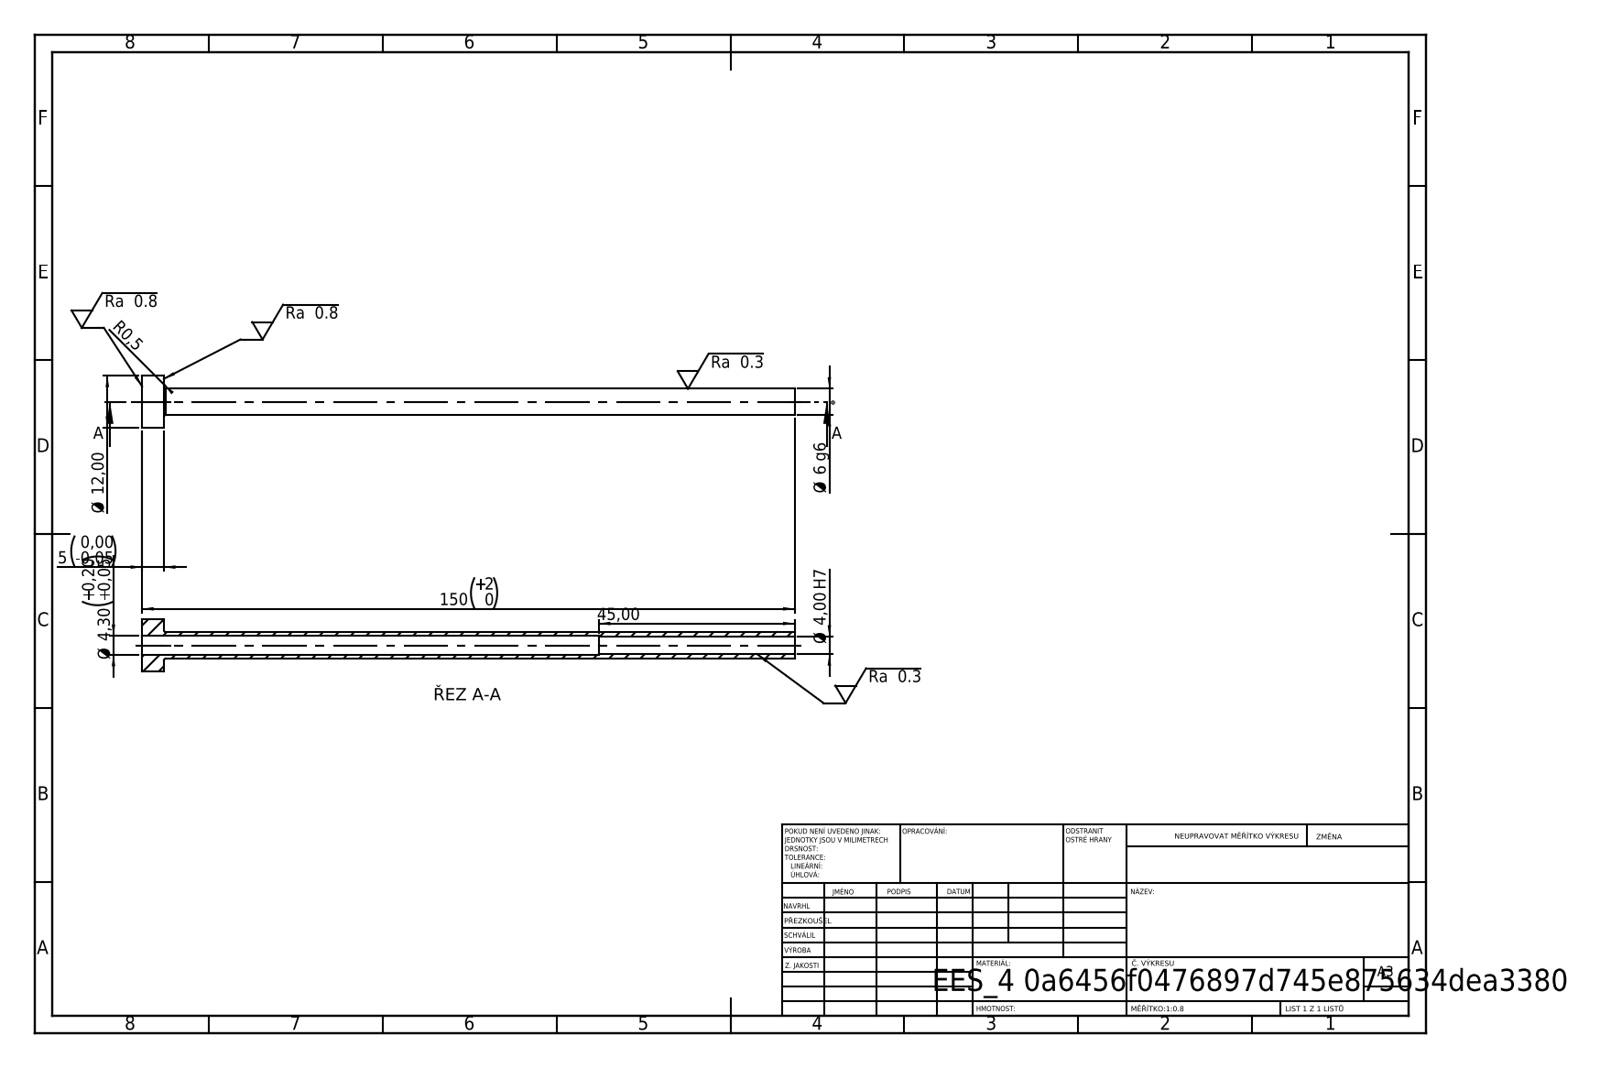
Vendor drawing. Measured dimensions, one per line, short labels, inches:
written by: SolidWorks 2019 (CONFIG_CONTROL_DESIGN)
unit: in
bodies: 1 solid, 14 faces (4 planar, 8 cylindrical, 2 other)
size: 5.906 × 0.472 × 0.472
volume: 0.157 in³; area: 7.91 in²
holes: 1× ⌀0.157, 1× ⌀0.169
bosses: 1× ⌀0.472, 1× ⌀0.236
face distances: 0.197, 5.906, 5.709, 4.134, 3.937, 1.772
